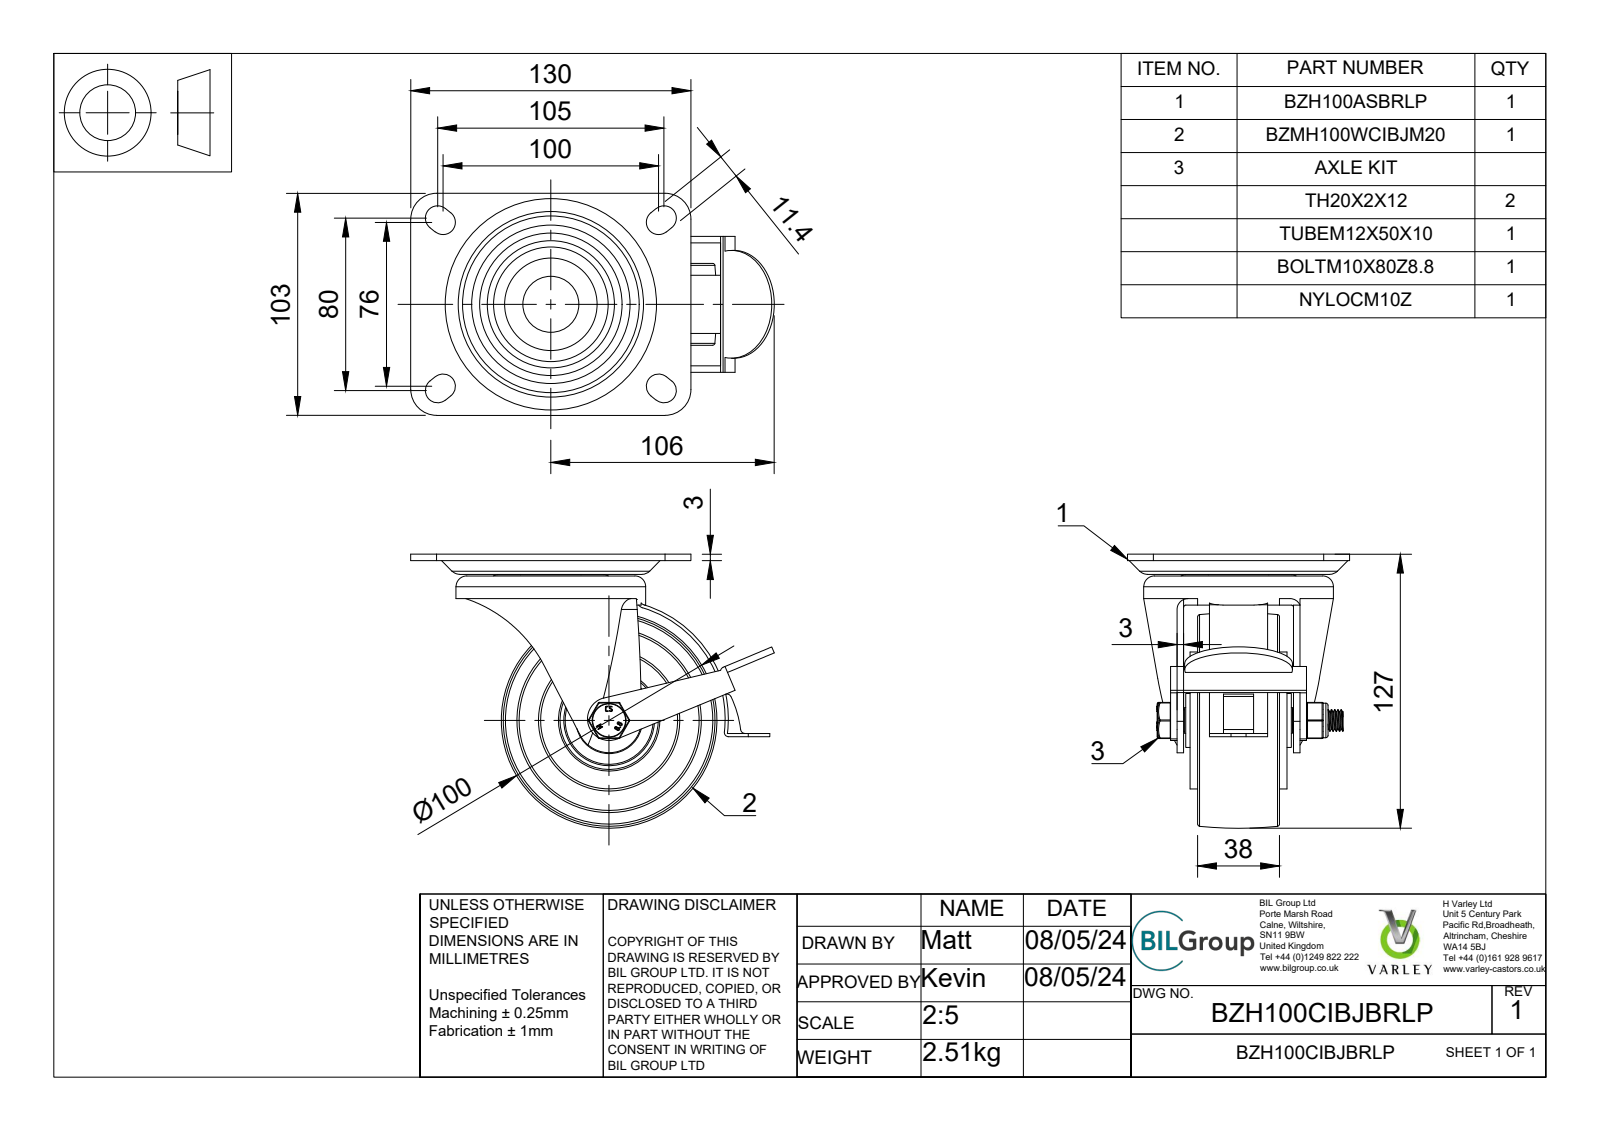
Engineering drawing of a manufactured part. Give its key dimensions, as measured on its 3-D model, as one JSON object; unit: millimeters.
{"part_name": "BZH100CIBJBRLP v3; BZH100ASBRLP v1; ZINC PLATED, PRESSED STEEL TOP PLATE; ZINC PLATED, PRESSED STEEL FORKS (+8 more)", "step_written_by": "Autodesk Translation Framework v12.20.1.177 (AUTOMOTIVE_DESIGN)", "units": "millimeters", "bodies": {"solids": 38, "faces": 1121, "planar": 440, "cylindrical": 232, "other": 449}, "overall_size": [168.66, 127.13, 103], "volume_mm3": 326539, "surface_area_mm2": 170060, "round_holes": [[10, 1], [10.2, 1], [10.5, 1], [12, 1], [12.2, 1], [20, 1], [28.5, 1], [30, 1], [30.8, 1], [40.3, 1], [40.5, 1], [42, 1]], "round_bosses_or_shafts": [[88, 1], [63.5, 1], [40.8, 1], [36, 1], [31.3, 1], [28, 1], [27, 1], [26, 1]], "partial_cylinders_radius": [[0.5, 18], [2, 8], [5.7, 8], [0.33, 4], [0.64, 4], [12, 4], [10, 3], [0.63, 2]], "face_to_face_distances": [3, 3.5, 27.5, 14, 6, 17.5, 51, 54, 9.5, 47.5]}
